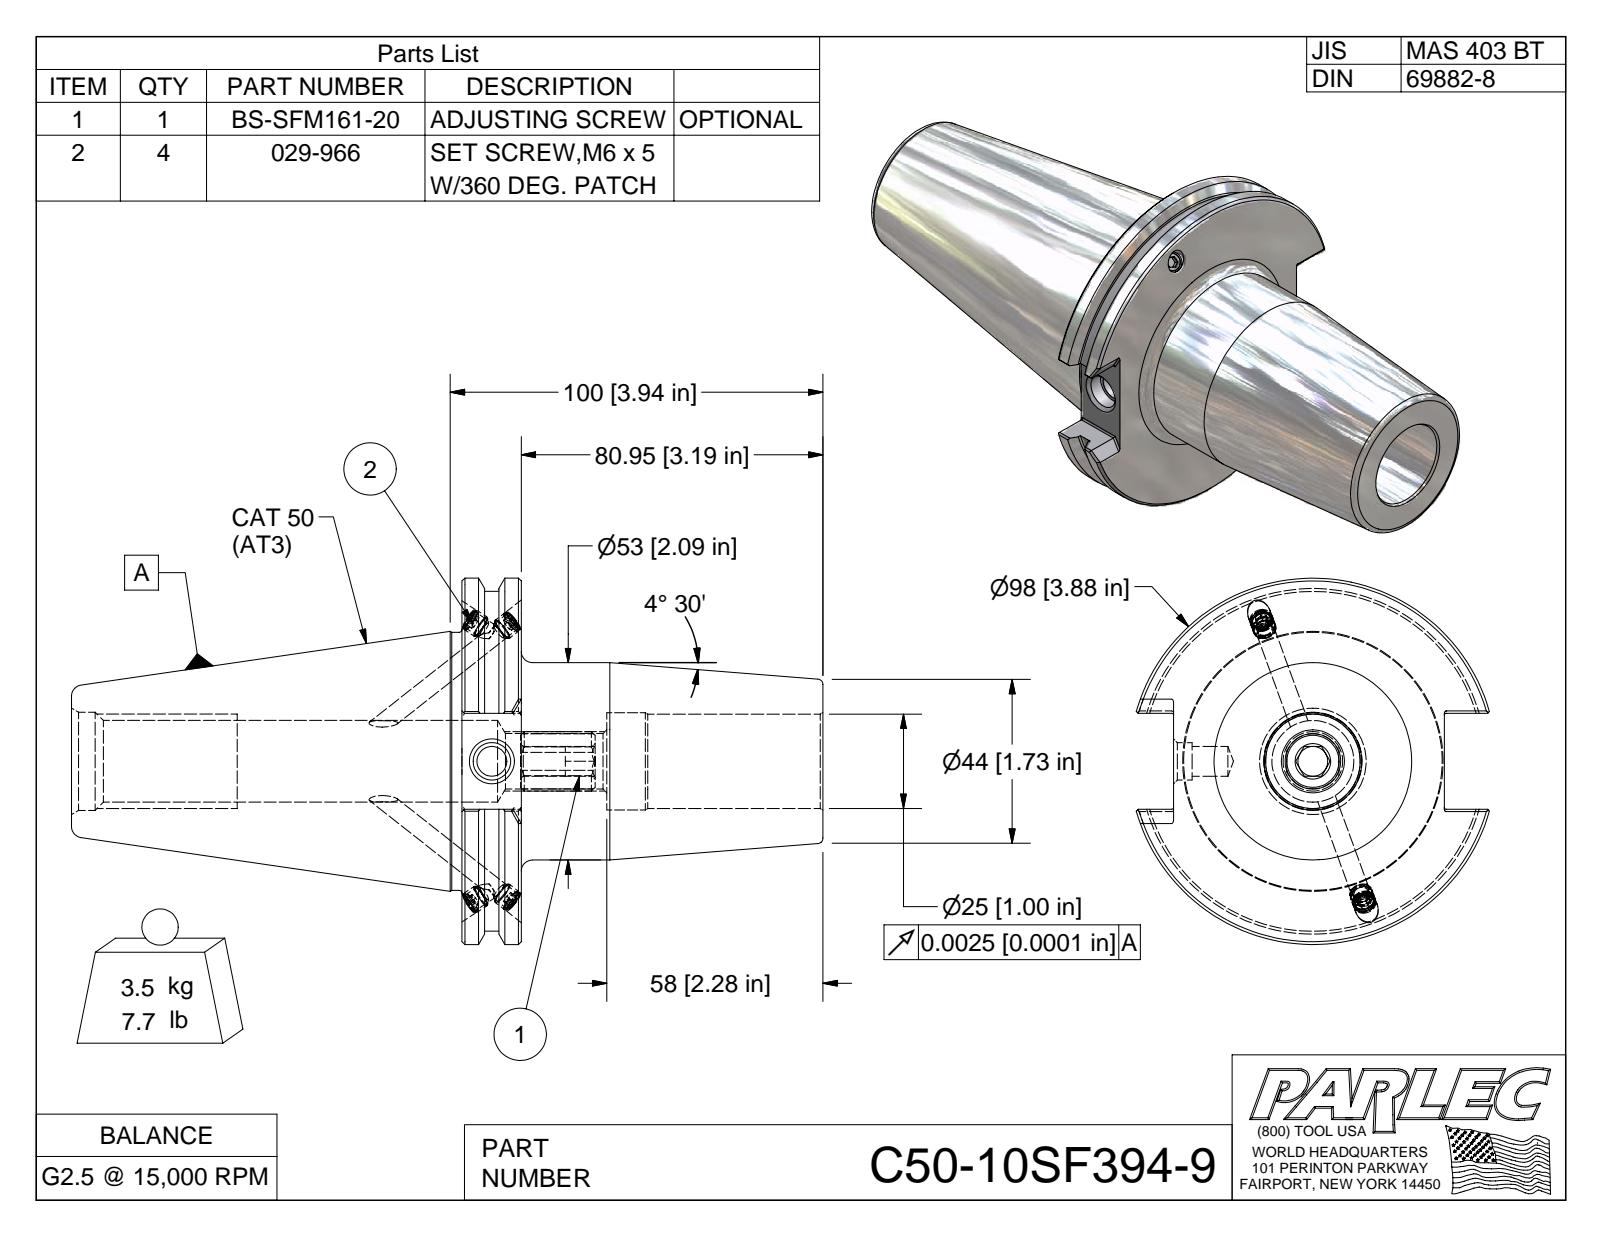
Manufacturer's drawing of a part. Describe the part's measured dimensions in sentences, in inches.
The part is named "C50-10SF394-9; C50BC-10SF394-9-1; BS-SFM161-20; 029-966". Its 3-D file was written by "Autodesk Inventor 2009 (AUTOMOTIVE_DESIGN)". It is 6 solids with 184 faces: 87 planar, 44 cylindrical and 53 other. Overall it measures 7.937 by 3.875 by 3.729 inches. Its volume is 27.11 cubic inches and its surface area 101.5 square inches. Round holes: 4 of diameter 0.197, 4 of diameter 0.24, 1 of diameter 0.999, 1 of diameter 1.029. Round bosses or shafts: 4 of diameter 0.244, 4 of diameter 0.236, 1 of diameter 3.875, 1 of diameter 3.594, 1 of diameter 2.73, 1 of diameter 2.087. Partial cylindrical surfaces (rounded edges, fillets, slot ends): 12 of radius 0.02, 1 of radius 0.315. The main face-to-face distances are 0.625, 3.812, 3.187, 4.125, 4.75, 7.937, 5.654, 1.529, 0.904, 2.283.
